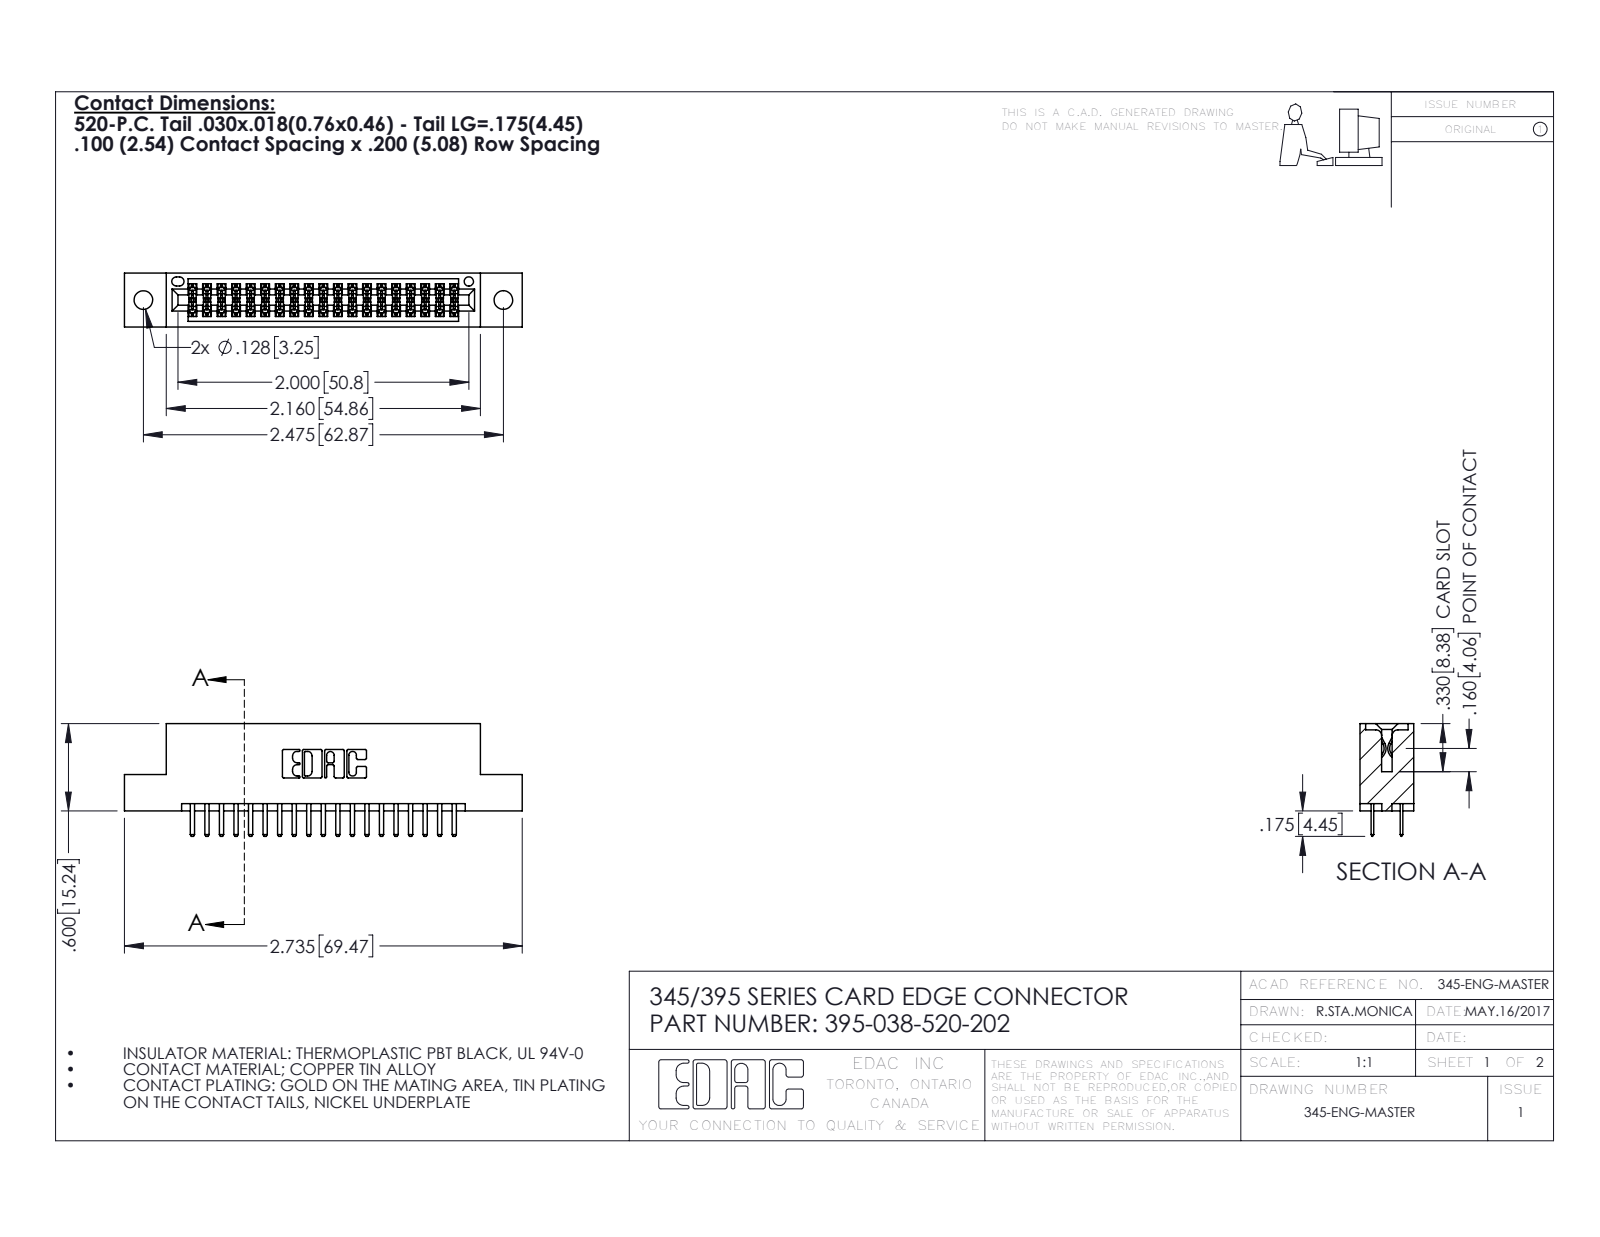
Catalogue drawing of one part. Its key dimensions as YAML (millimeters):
part_name: "395-038-520-202; 345 Part_Flush Mounting Lugs - 0.128 Dia; 345-292-001_345-293-120"
step_written_by: "SolidWorks 2016 (CONFIG_CONTROL_DESIGN)"
units: millimeters
bodies: {solids: 39, faces: 2178, planar: 1410, cylindrical: 768, other: 0}
overall_size: [69.5, 19.7, 9.4]
volume: 6490
surface_area: 8826
round_holes:
  - {diameter: 3.3, count: 2}
  - {diameter: 1.6, count: 1}
partial_cylinders:
  - {radius: 0.2, count: 57}
  - {radius: 0.3, count: 42}
  - {radius: 0.3, count: 22}
  - {radius: 0.2, count: 6}
  - {radius: 0.8, count: 6}
  - {radius: 0.7, count: 3}
  - {radius: 0.4, count: 2}
  - {radius: 0.5, count: 2}
face_to_face_distances: [5.1, 7.6, 1.8, 9.4, 2.5, 6.9, 0.6, 5.7, 0.6, 1.8]
hole_center_spacings: [6.9, 56.9, 62.9]
